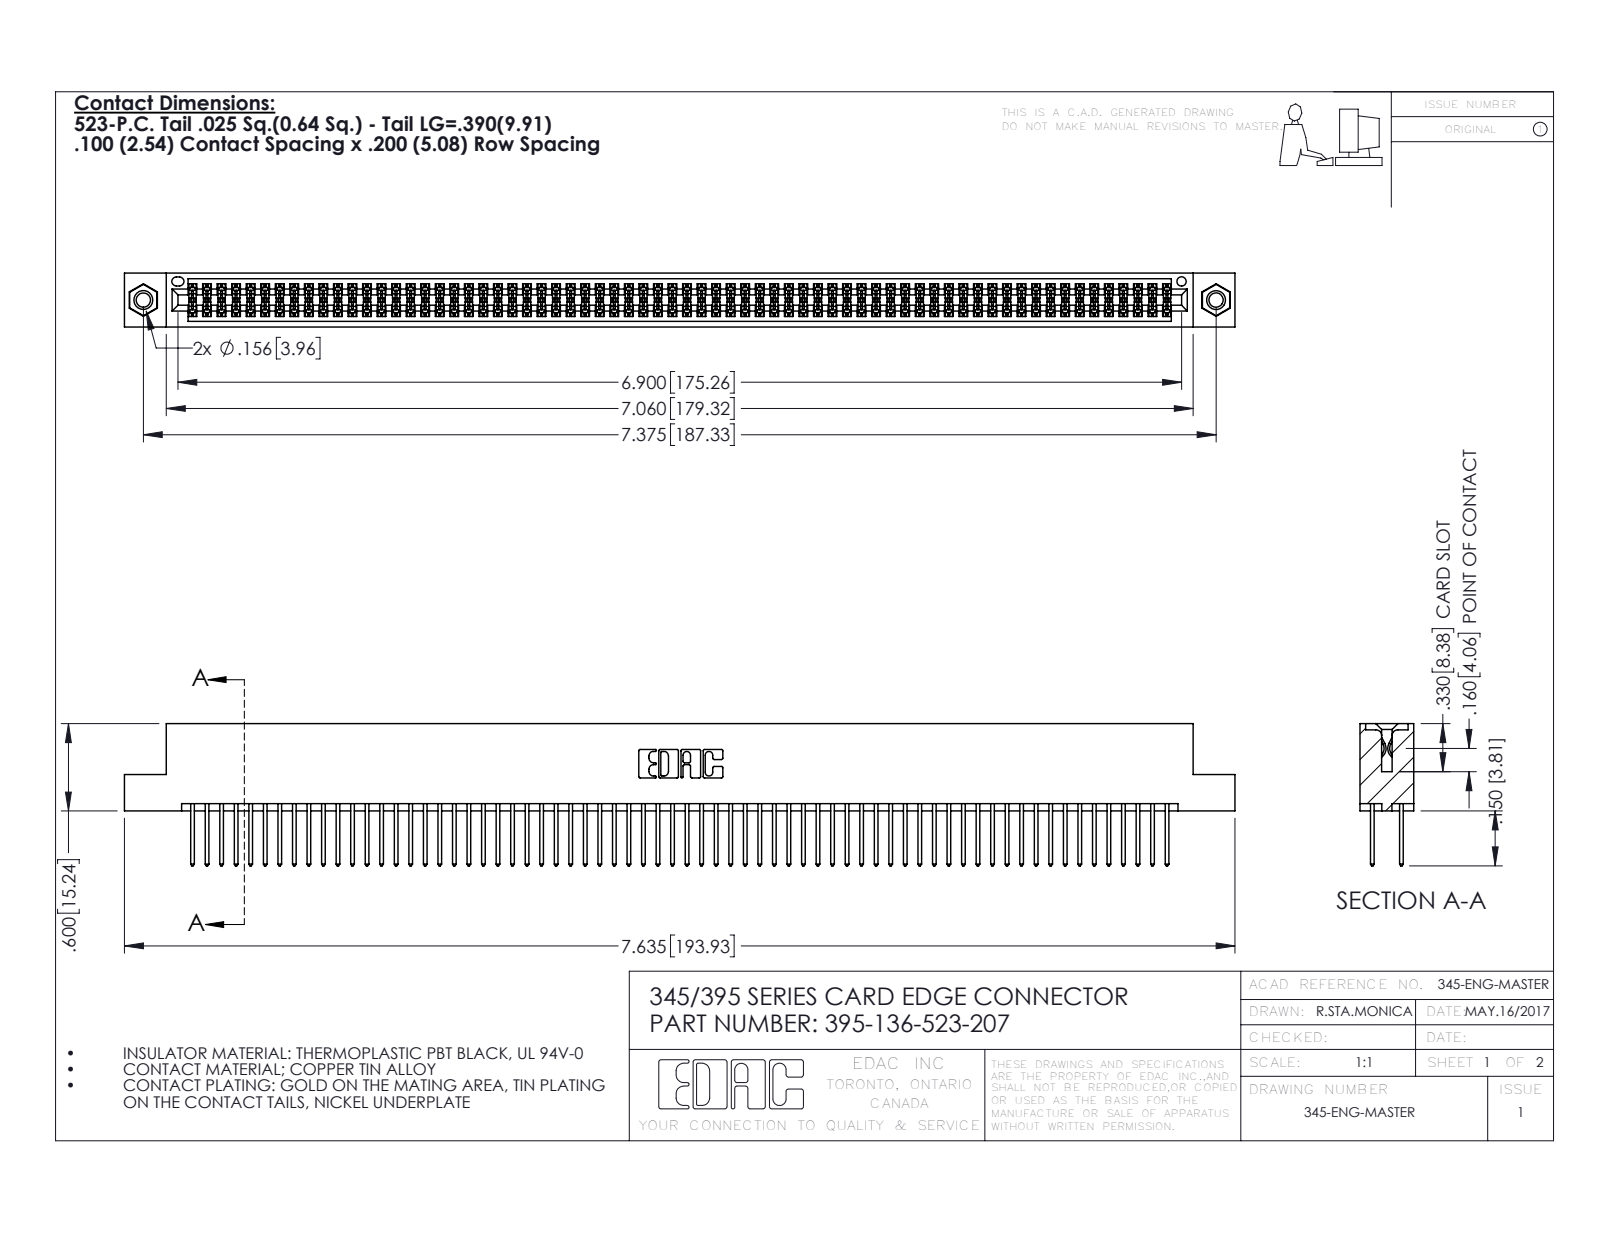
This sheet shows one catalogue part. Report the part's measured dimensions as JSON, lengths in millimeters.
{"part_name": "345-292-001_345-293-123; 345-250-001_345-250-005-103; 345 Part_Flush Mounting Lugs - 0.156 Dia-TI; 395-136-523-207", "step_written_by": "SolidWorks 2016 (CONFIG_CONTROL_DESIGN)", "units": "millimeters", "bodies": {"solids": 139, "faces": 6986, "planar": 4600, "cylindrical": 2370, "other": 16}, "overall_size": [193.9, 24.8, 9.4], "volume_mm3": 19350, "surface_area_mm2": 30370, "round_holes": [[2.5, 2], [3.2, 2], [4, 2], [1.6, 1]], "round_bosses_or_shafts": [[3.9, 2]], "partial_cylinders_radius": [[0.2, 204], [0.3, 136], [0.3, 22], [0.2, 6], [0.8, 6], [0.7, 3], [0.4, 2], [0.5, 2]], "face_to_face_distances": [1.8, 7.6, 5.1, 2.5, 6.9, 0.6, 9.4, 5.7, 4.4, 3.8], "hole_center_spacings": [6.9, 181.3, 187.3]}
